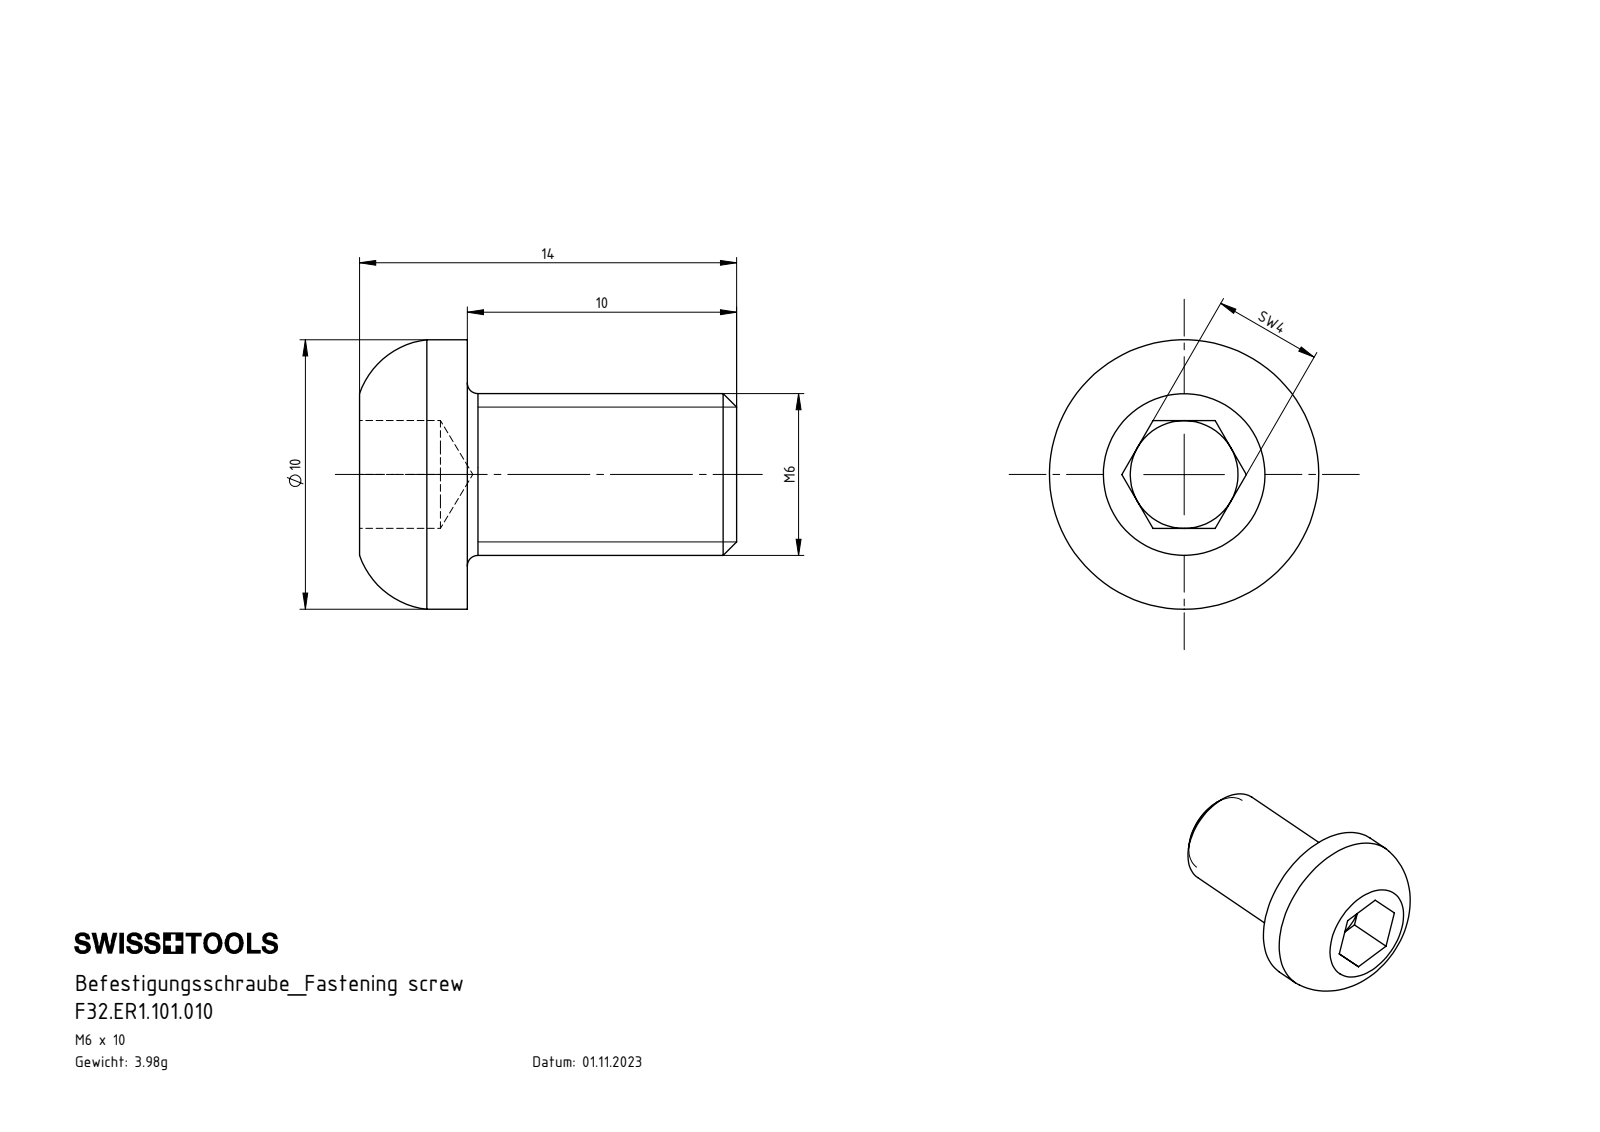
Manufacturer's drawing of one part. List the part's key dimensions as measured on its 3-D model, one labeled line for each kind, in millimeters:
Part name (STEP PRODUCT): F32.ER1.101.010
STEP written by: SolidWorks 2017 (AUTOMOTIVE_DESIGN)
Units: millimetres
Bodies: 1 solid, 27 faces (15 planar, 4 cylindrical, 8 other)
Overall size (bounding box): 14 × 10 × 10
Volume: 507 mm³ · Surface area: 467 mm²
Round bosses / shafts (diameter × count): ⌀10 ×1, ⌀6 ×1
Main face-to-face distances: 4, 10, 14, 3, 1, 11
